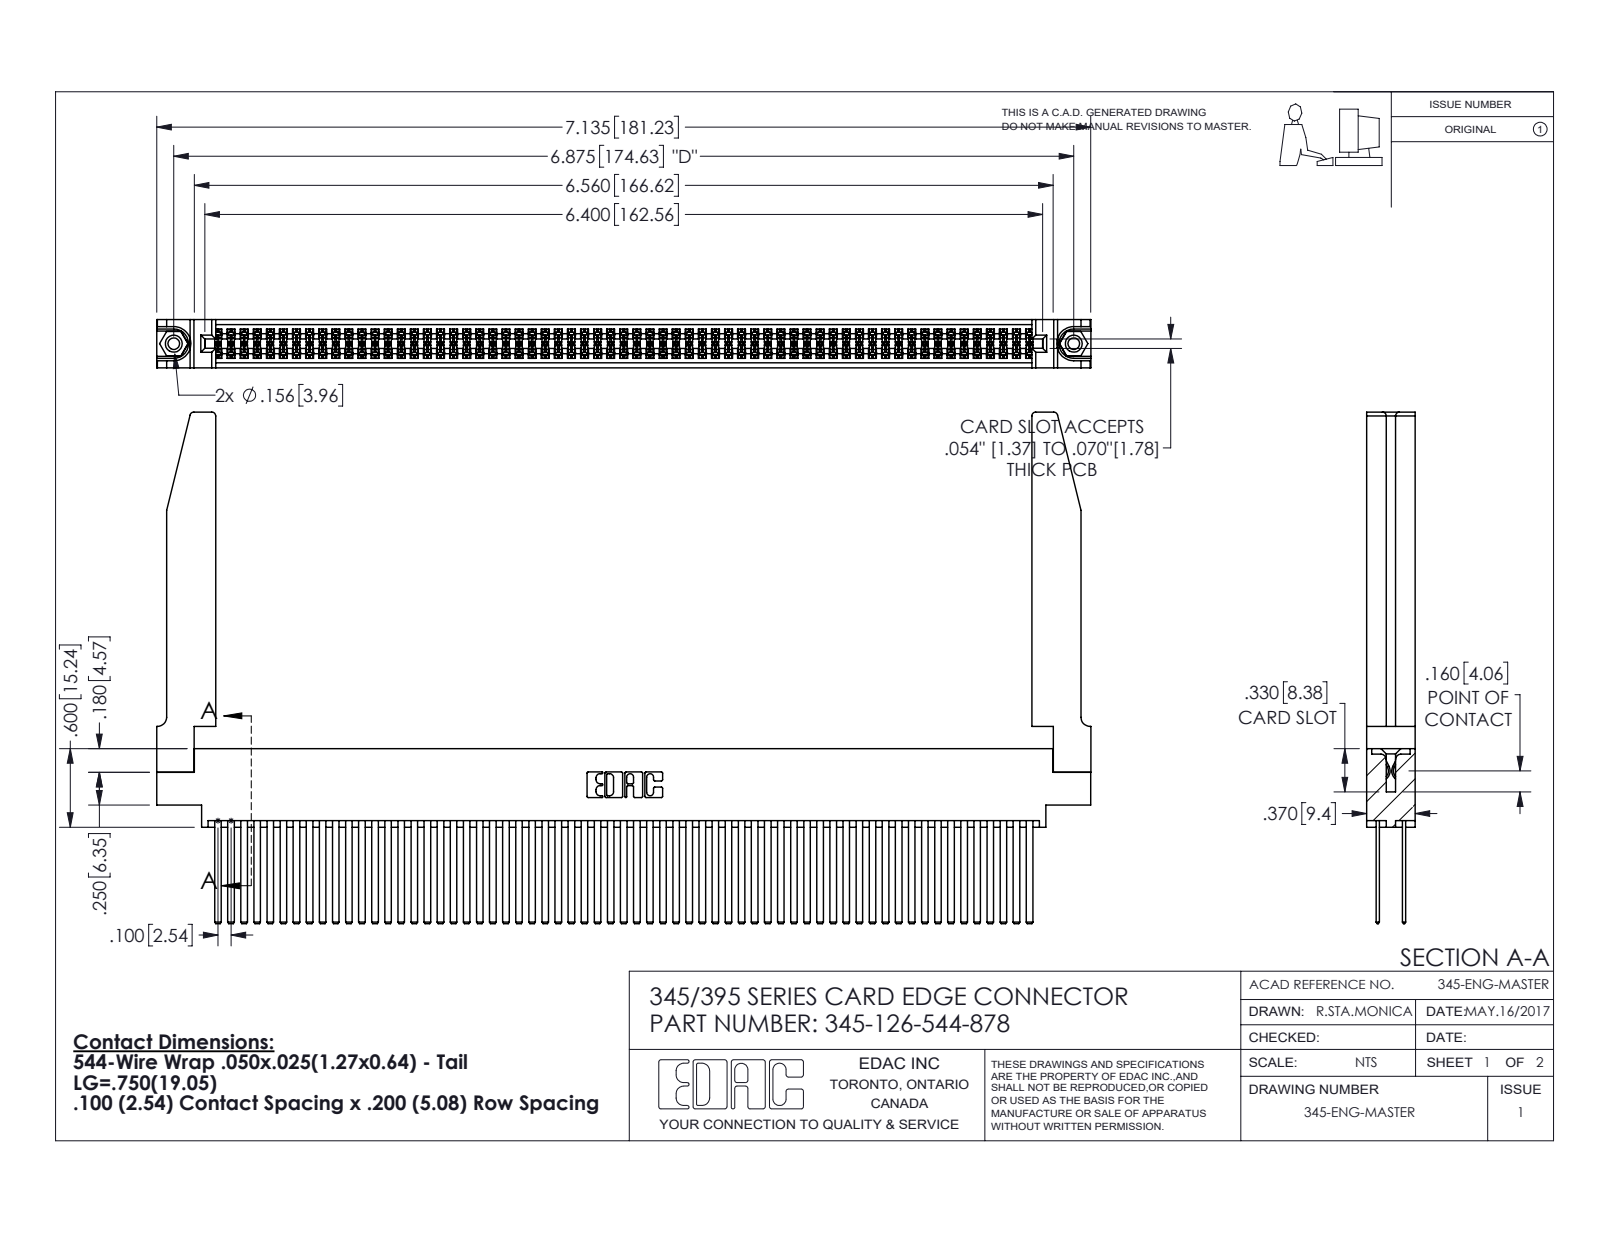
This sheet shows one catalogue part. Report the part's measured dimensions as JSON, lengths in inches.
{"part_name": "345-126-544-878; 345-220-078_345-220-078; 345-250-001_345-250-001-102; 345-292-001_345-293-144 (+1 more)", "step_written_by": "SolidWorks 2016 (CONFIG_CONTROL_DESIGN)", "units": "inches", "bodies": {"solids": 131, "faces": 5908, "planar": 3880, "cylindrical": 1976, "other": 52}, "overall_size": [7.136, 3.907, 0.37], "volume_in3": 1.661, "surface_area_in2": 64.05, "round_holes": [[0.089, 2], [0.125, 2], [0.156, 2], [0.064, 1]], "round_bosses_or_shafts": [[0.155, 2]], "partial_cylinders_radius": [[0.006, 189], [0.01, 22], [0.03, 8], [0.007, 6], [0.031, 6], [0.026, 3], [0.014, 2], [0.019, 2]], "face_to_face_distances": [0.072, 0.298, 0.098, 0.272, 0.025, 0.2, 0.37, 0.225, 0.175, 0.148], "hole_center_spacings": [0.27, 6.639, 6.875]}
